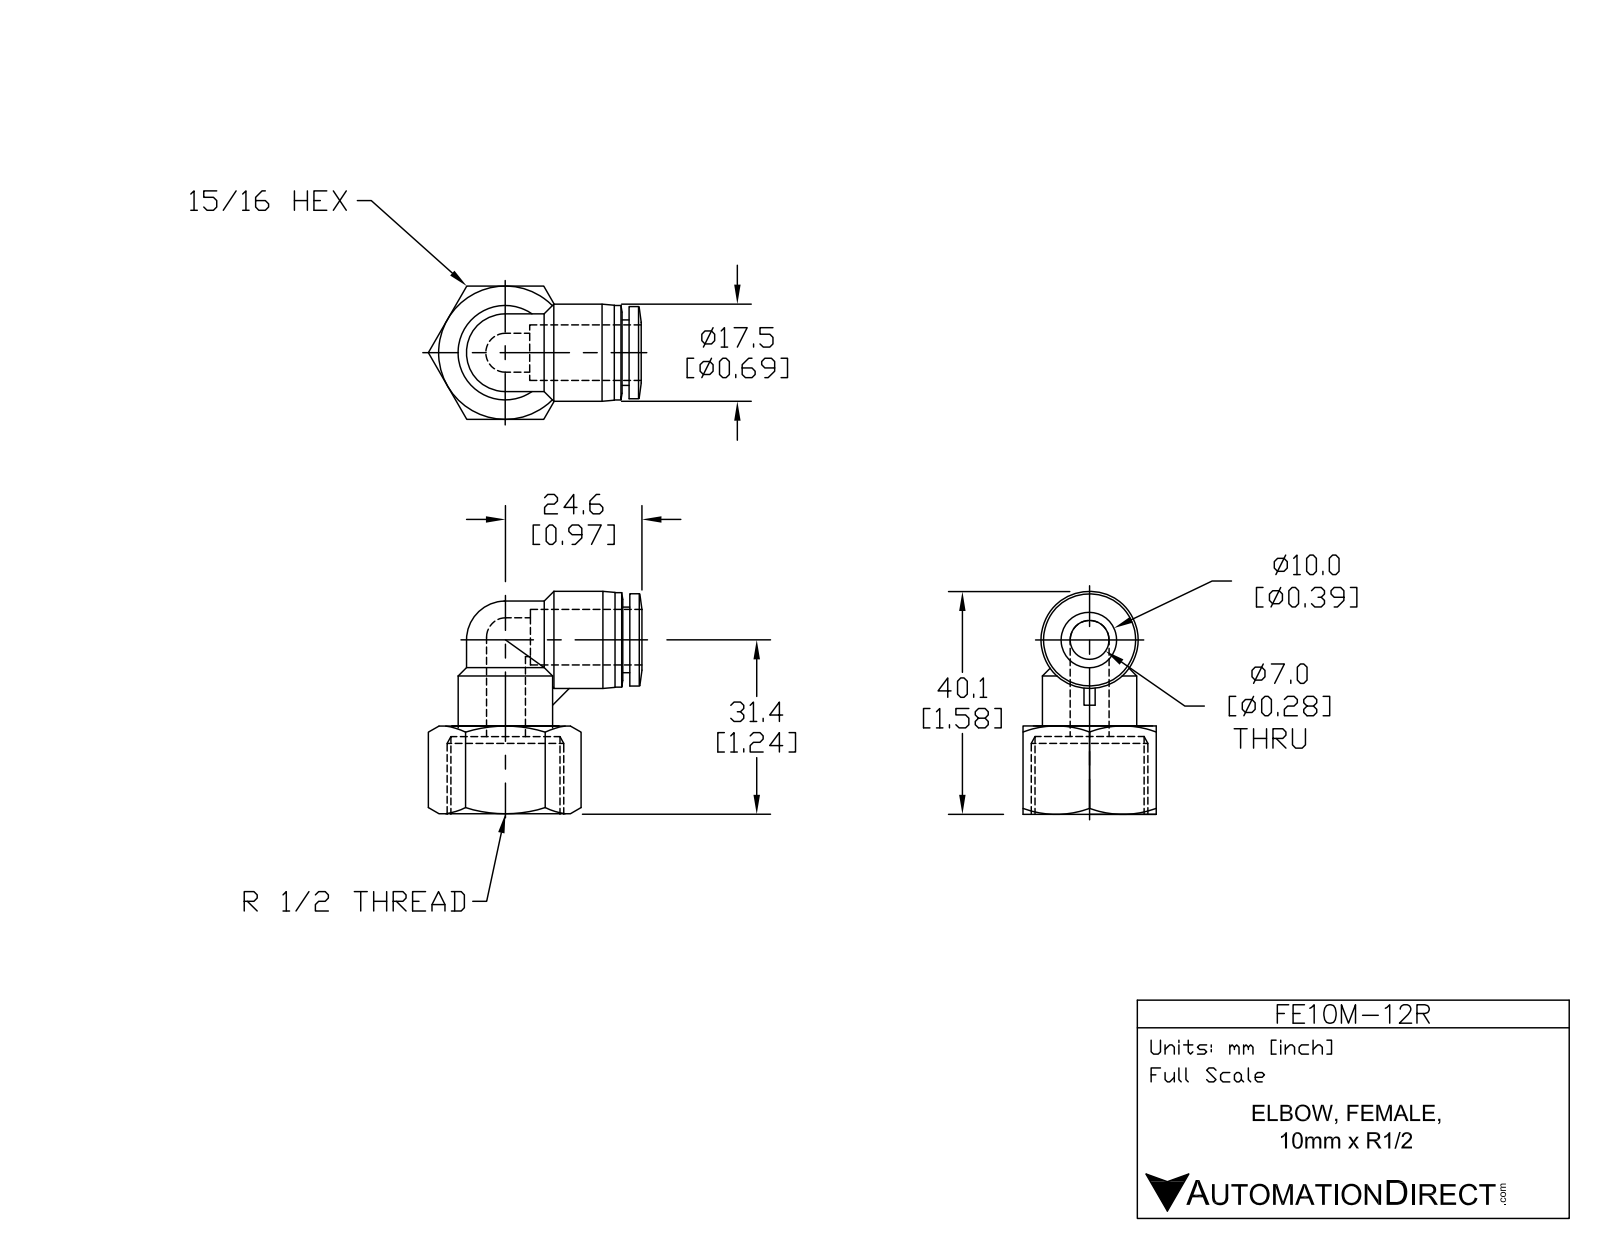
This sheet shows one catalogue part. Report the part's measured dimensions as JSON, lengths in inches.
{"part_name": "FE10M-12R", "step_written_by": "SolidWorks 2015 (AUTOMOTIVE_DESIGN)", "units": "inches", "bodies": {"solids": 1, "faces": 70, "planar": 17, "cylindrical": 20, "other": 33}, "overall_size": [1.585, 1.514, 0.945], "volume_in3": 0.534, "surface_area_in2": 9.902, "round_holes": [[0.276, 2], [0.406, 1]], "round_bosses_or_shafts": [[0.669, 2], [0.689, 1], [0.654, 1], [0.551, 1], [0.465, 1]], "partial_cylinders_radius": [[0.276, 1]], "face_to_face_distances": [0.945, 0.079, 0.551, 0.63, 0.049, 0.659, 0.709, 0.433, 0.512, 0.604]}
